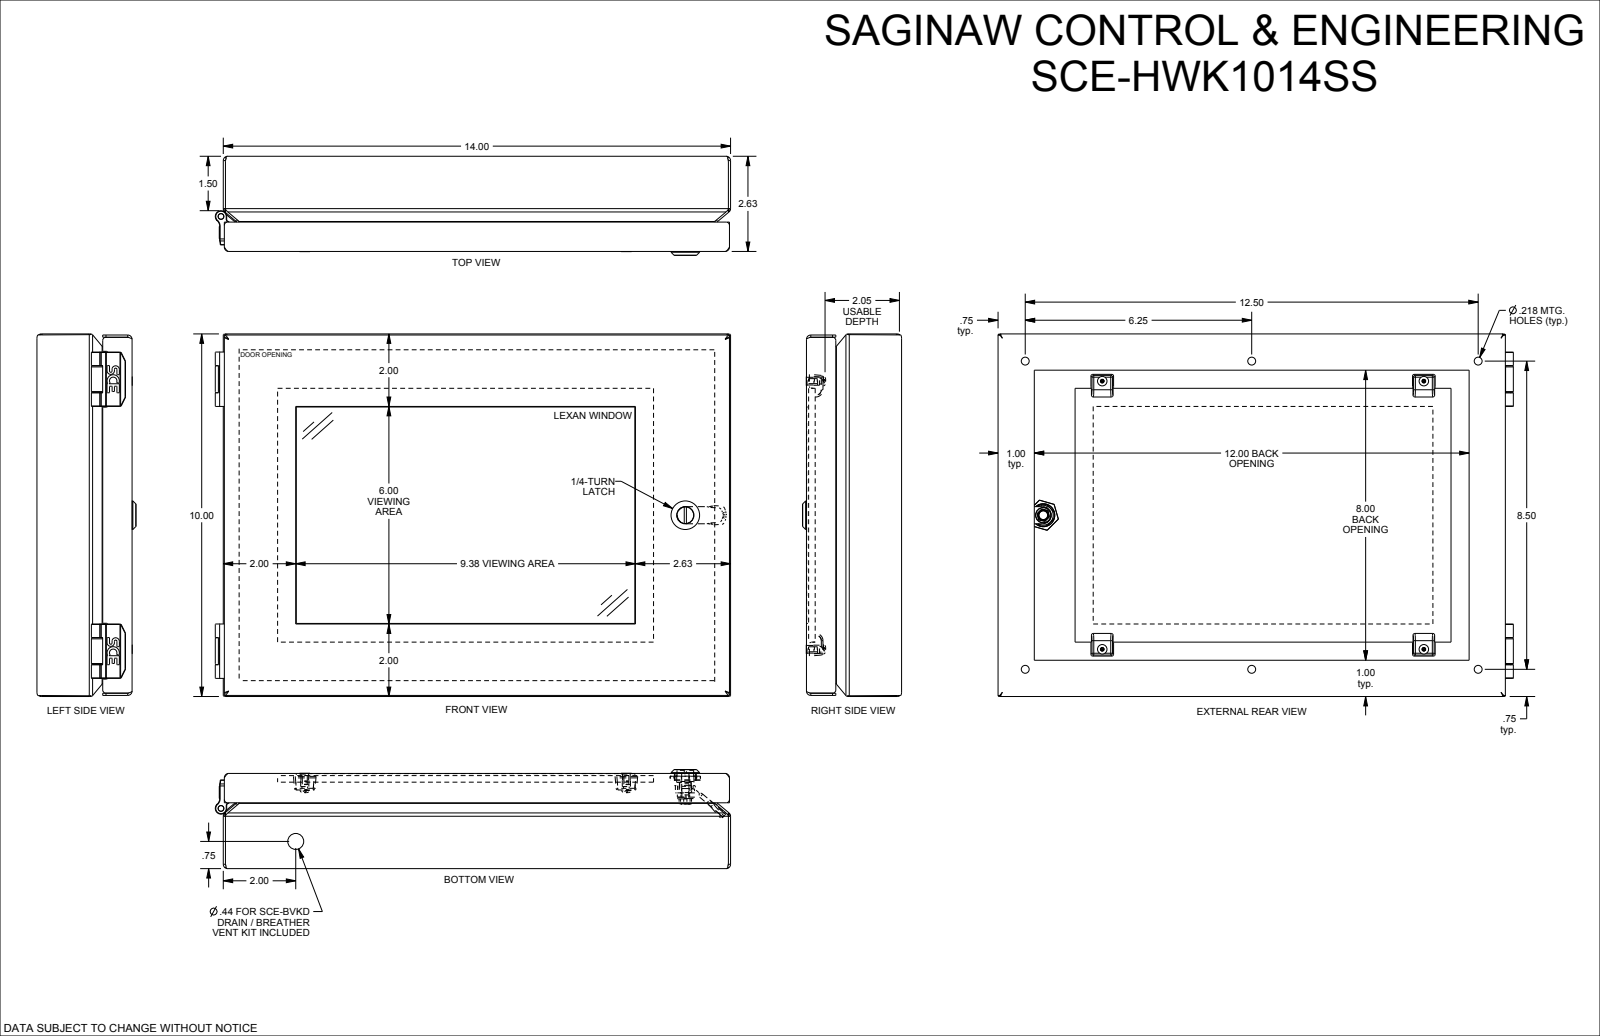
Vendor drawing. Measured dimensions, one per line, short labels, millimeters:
name: SCE-HWK1014
written by: SolidWorks 2021 (AUTOMOTIVE_DESIGN)
unit: mm
bodies: 24 solids, 1167 faces (461 planar, 292 cylindrical, 414 other)
size: 361.2 × 254 × 69.4
volume: 600 300 mm³; area: 510 000 mm²
holes: 6× ⌀7.2, 4× ⌀4.1, 2× ⌀0.5, 2× ⌀2.5, 2× ⌀6.8, 1× ⌀4, 1× ⌀4.8, 1× ⌀5.1, 1× ⌀6.1, 1× ⌀6.5, 1× ⌀6.8, 1× ⌀7.2
bosses: 4× ⌀12.3, 4× ⌀6, 4× ⌀4.1, 2× ⌀6.6, 2× ⌀4.6, 1× ⌀20, 1× ⌀13.9, 1× ⌀11.7
rounds: 28× R0.8, 24× R0.2, 21× R0.3, 16× R1.3, 14× R0.3, 9× R0.5, 8× R1.6, 6× R1.5
face distances: 1.5, 1.5, 4.6, 6.1, 6, 1.4, 60.6, 65.2, 66.5, 66.7
hole spacings: 190.5, 158.8, 268, 215.9, 0.4, 108.7, 181.7, 317.5
